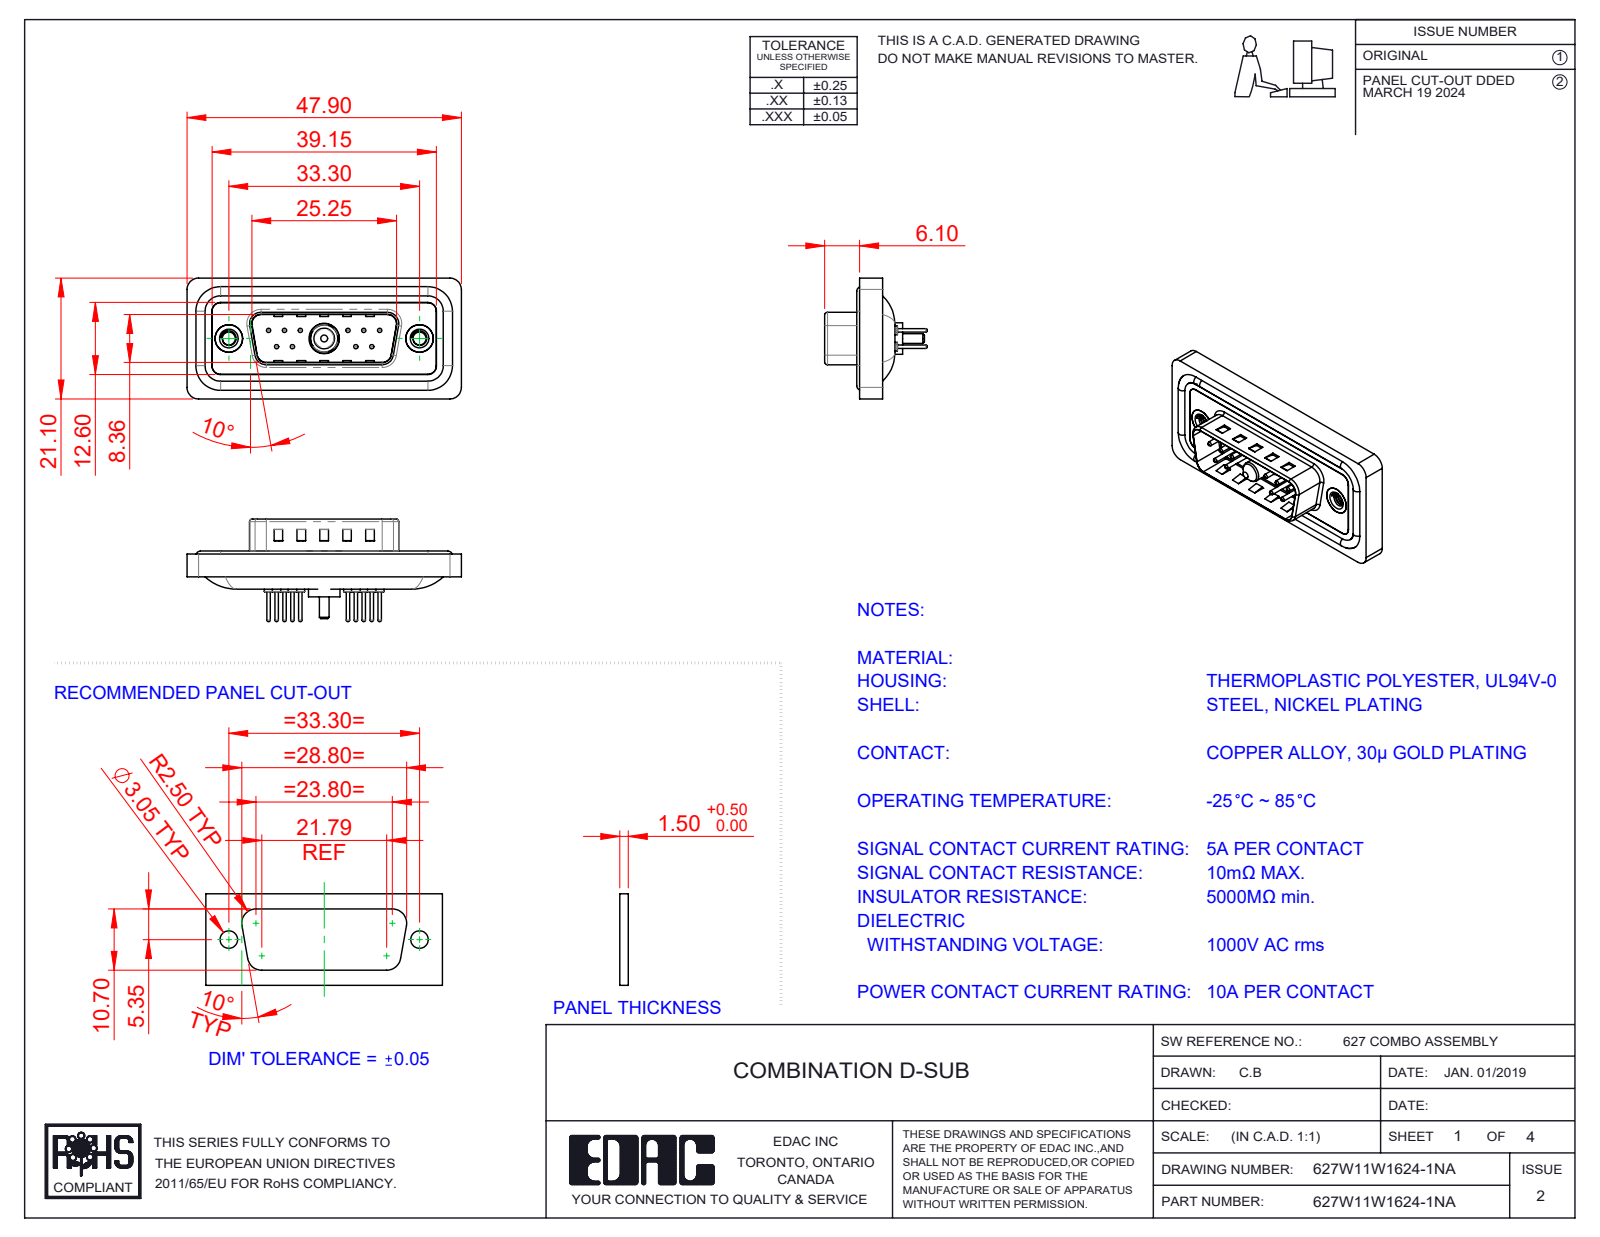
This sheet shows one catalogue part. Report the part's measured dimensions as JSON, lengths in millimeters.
{"part_name": "627Combo Contact Row 2_24; 627Combo Housing_11W1; 627Combo Shell Rear_15 Contacts; 627W11W1624-1NA (+5 more)", "step_written_by": "SolidWorks 2023 (CONFIG_CONTROL_DESIGN)", "units": "millimeters", "bodies": {"solids": 19, "faces": 867, "planar": 266, "cylindrical": 349, "other": 252}, "overall_size": [47.9, 21.1, 17.9], "volume_mm3": 5435, "surface_area_mm2": 8821, "round_holes": [[0.75, 10], [1.6, 10], [2, 10], [2.26, 2], [4, 2], [4.8, 2], [5, 2], [4.85, 1], [5.3, 1]], "round_bosses_or_shafts": [[1.5, 10], [0.6, 10], [1.6, 4], [4.9, 2], [5.5, 1], [5.2, 1], [4.75, 1], [3.75, 1]], "partial_cylinders_radius": [[1.5, 26], [2, 20], [0.5, 8], [1.6, 8], [1, 7], [0.25, 4], [0.6, 4], [0.65, 4]], "face_to_face_distances": [0.4, 1.1, 1.6, 1.5, 3.1, 0.5, 2.9, 2.5, 4.1, 0.82], "hole_center_spacings": [3.16, 2.77, 13.85, 11.08, 16.62, 5.03, 5.04, 5.54]}
